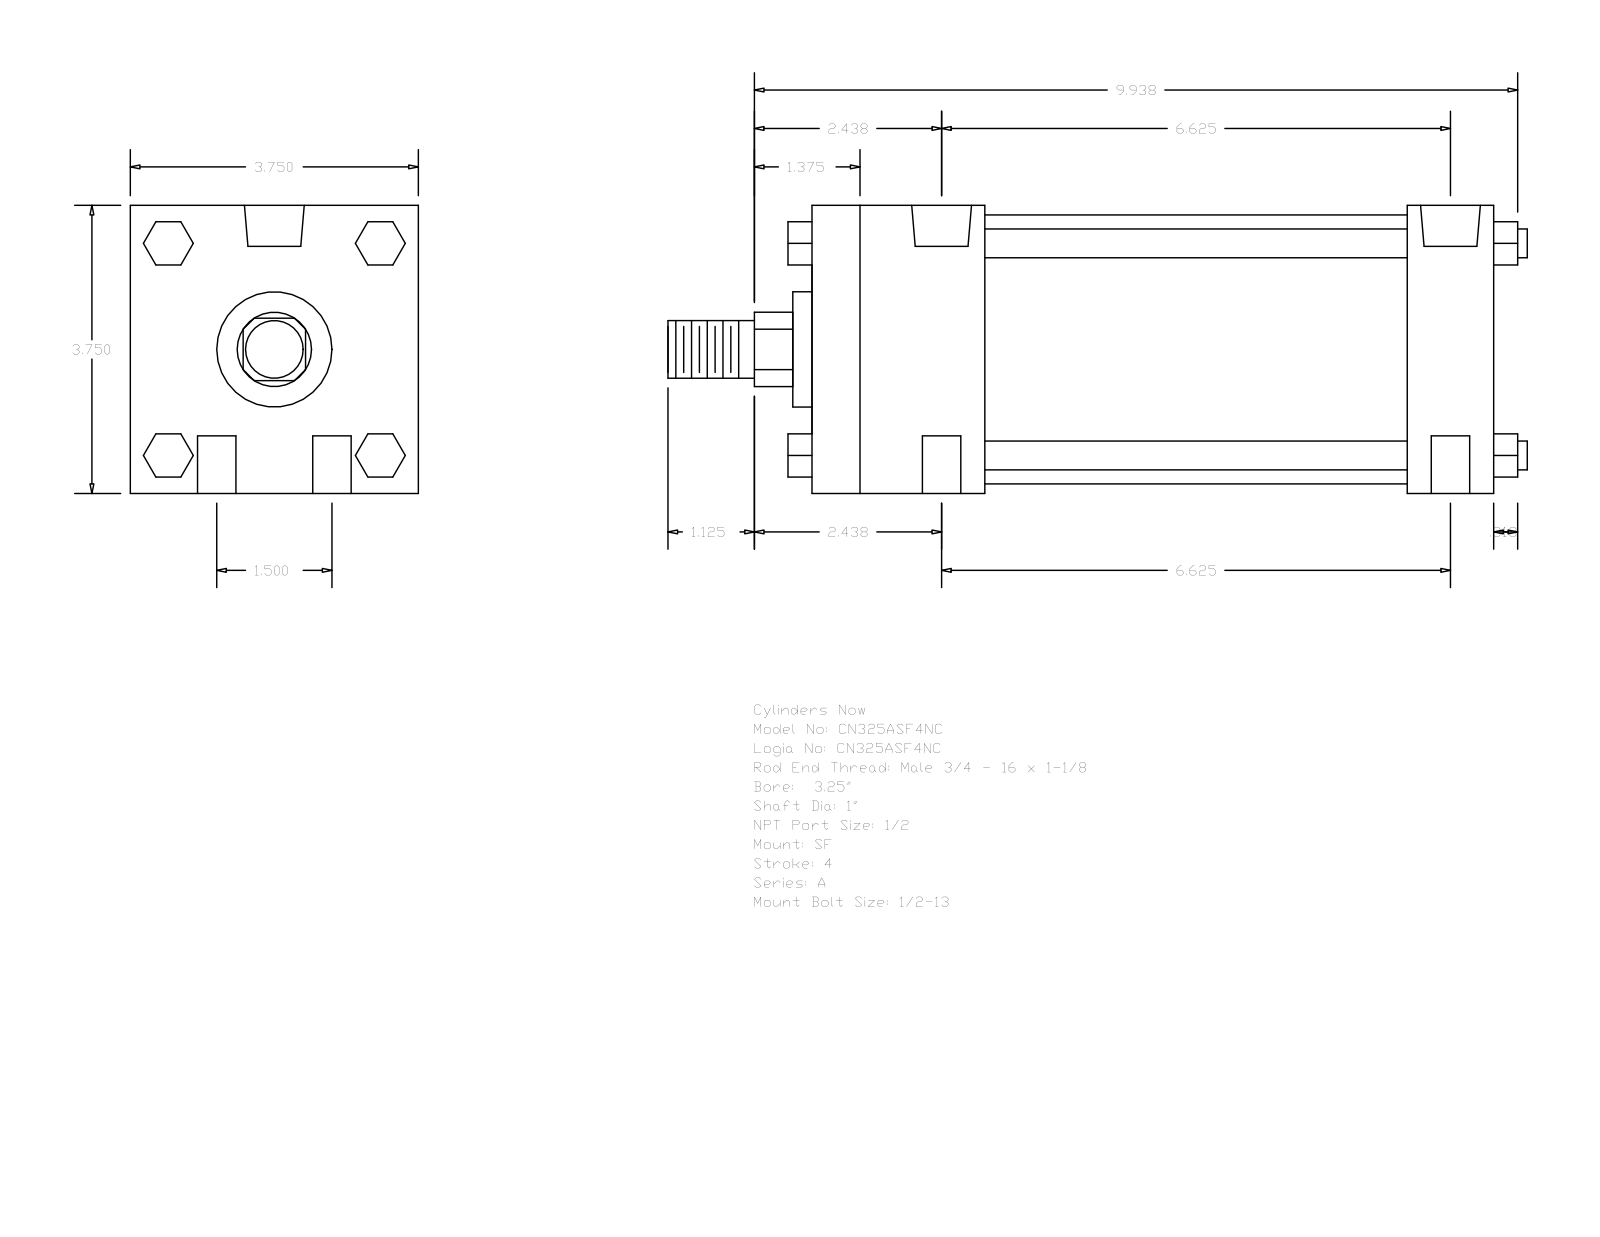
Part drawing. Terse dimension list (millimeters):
name: A_SF__0325_1
written by: GSSL Pune (CONFIG_CONTROL_DESIGN)
unit: mm
bodies: 0 solids, 124 faces (94 planar, 30 cylindrical, 0 other)
size: 284.16 × 95.25 × 95.25
holes: 4× ⌀12.7, 2× ⌀8.73, 2× ⌀19.77
bosses: 4× ⌀9.53, 1× ⌀88.9, 1× ⌀38.1, 1× ⌀25.4, 1× ⌀19.05
rounds: 1× R12.29
face distances: 95.24, 225.42, 28.57, 196.85, 57.15, 139.7, 168.27, 14.28, 35.05, 60.71
hole spacings: 19.05, 169.35, 168.28, 38.1, 172.54, 161.92
